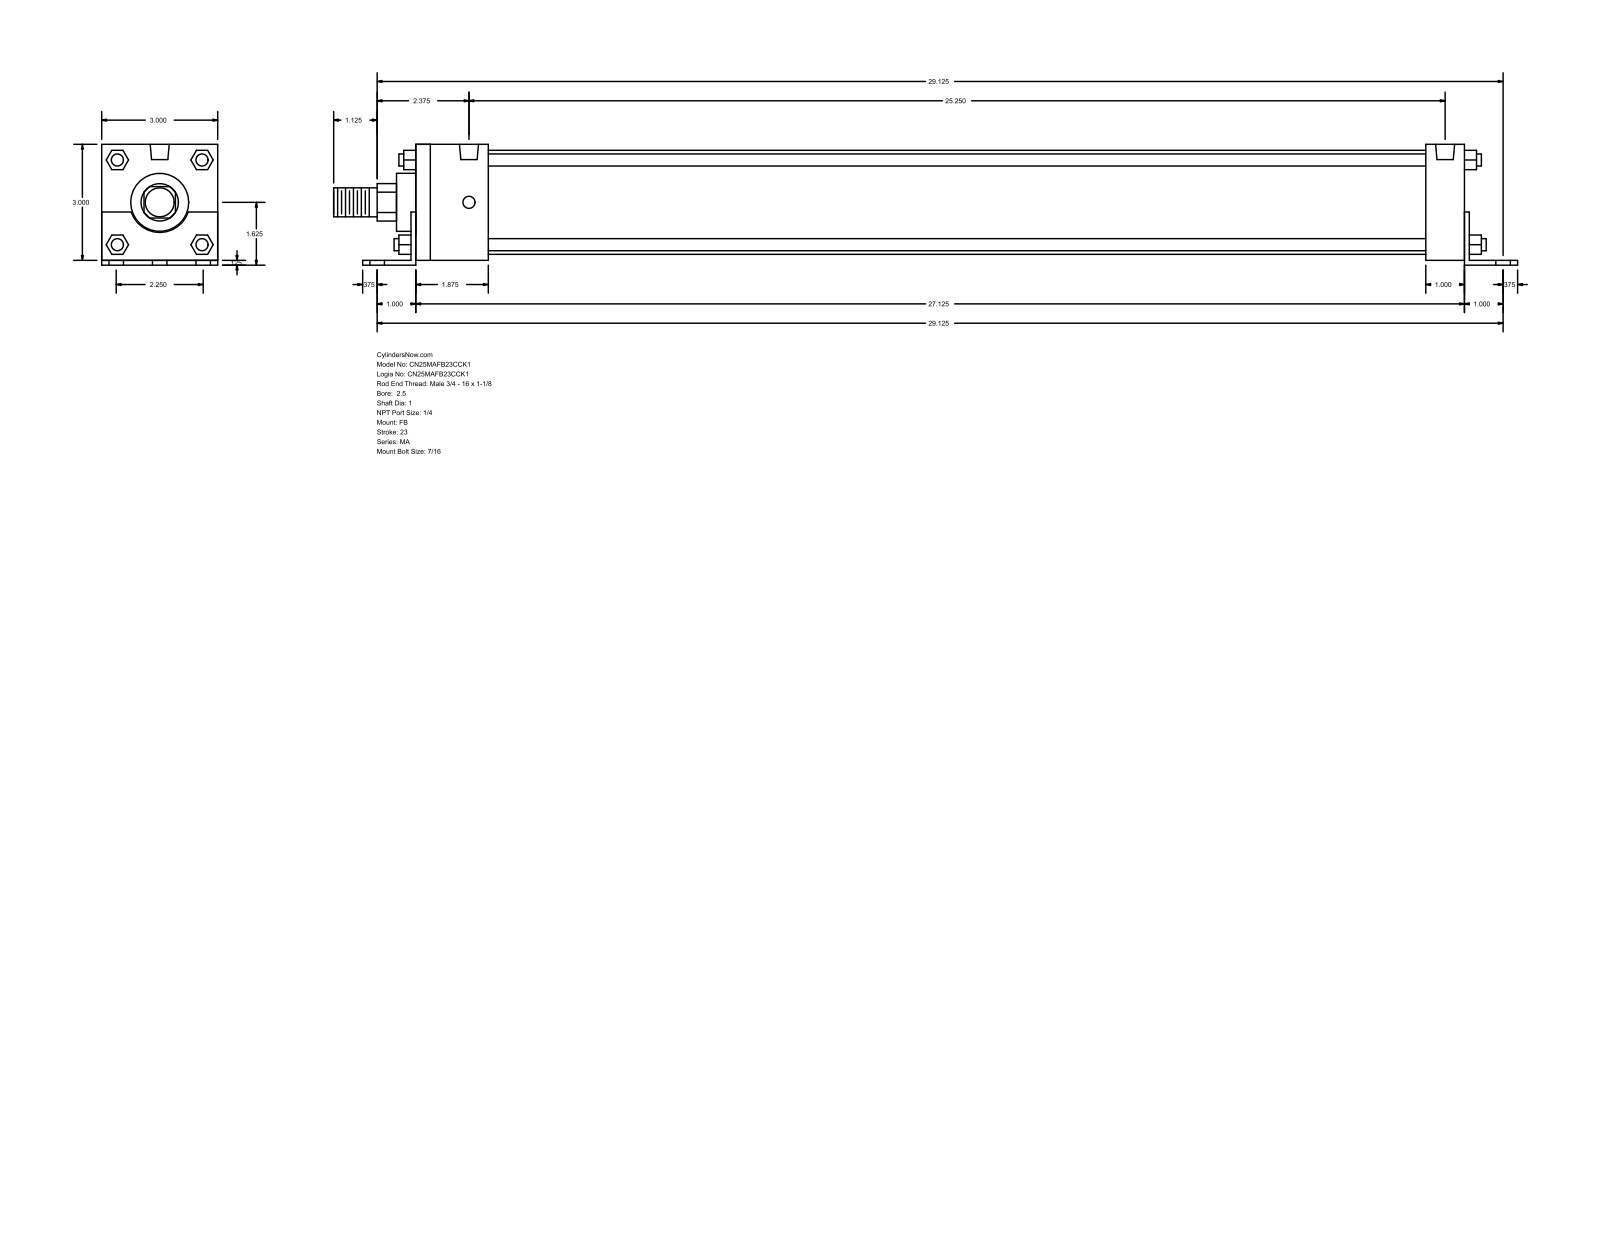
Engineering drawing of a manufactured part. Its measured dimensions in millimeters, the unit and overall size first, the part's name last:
Units: millimetres
Overall size (bounding box): 777.88 × 79.38 × 76.2
Round holes (diameter × count): ⌀11.11 ×6, ⌀7.94 ×4, ⌀12.49 ×2
Round bosses / shafts (diameter × count): ⌀7.94 ×4, ⌀68.33 ×1, ⌀38.1 ×1, ⌀25.4 ×1, ⌀19.05 ×1
Partial cylindrical surfaces — rounded edges, fillets, slot ends (radius × count): R12.29 ×1, R19.81 ×1
Main face-to-face distances: 76.2, 3.17, 79.37, 692.15, 688.98, 12.7, 28.57, 25.4, 50.8, 47.63
Hole centre spacings: 28.57, 740.32, 739.77, 47.62, 57.14, 66.75, 641.34, 680.04
Bodies: 0 solids, 140 faces (105 planar, 35 cylindrical, 0 other)
Part name (STEP PRODUCT): MA_FB__0250_1
STEP written by: GSSL Pune (CONFIG_CONTROL_DESIGN)
